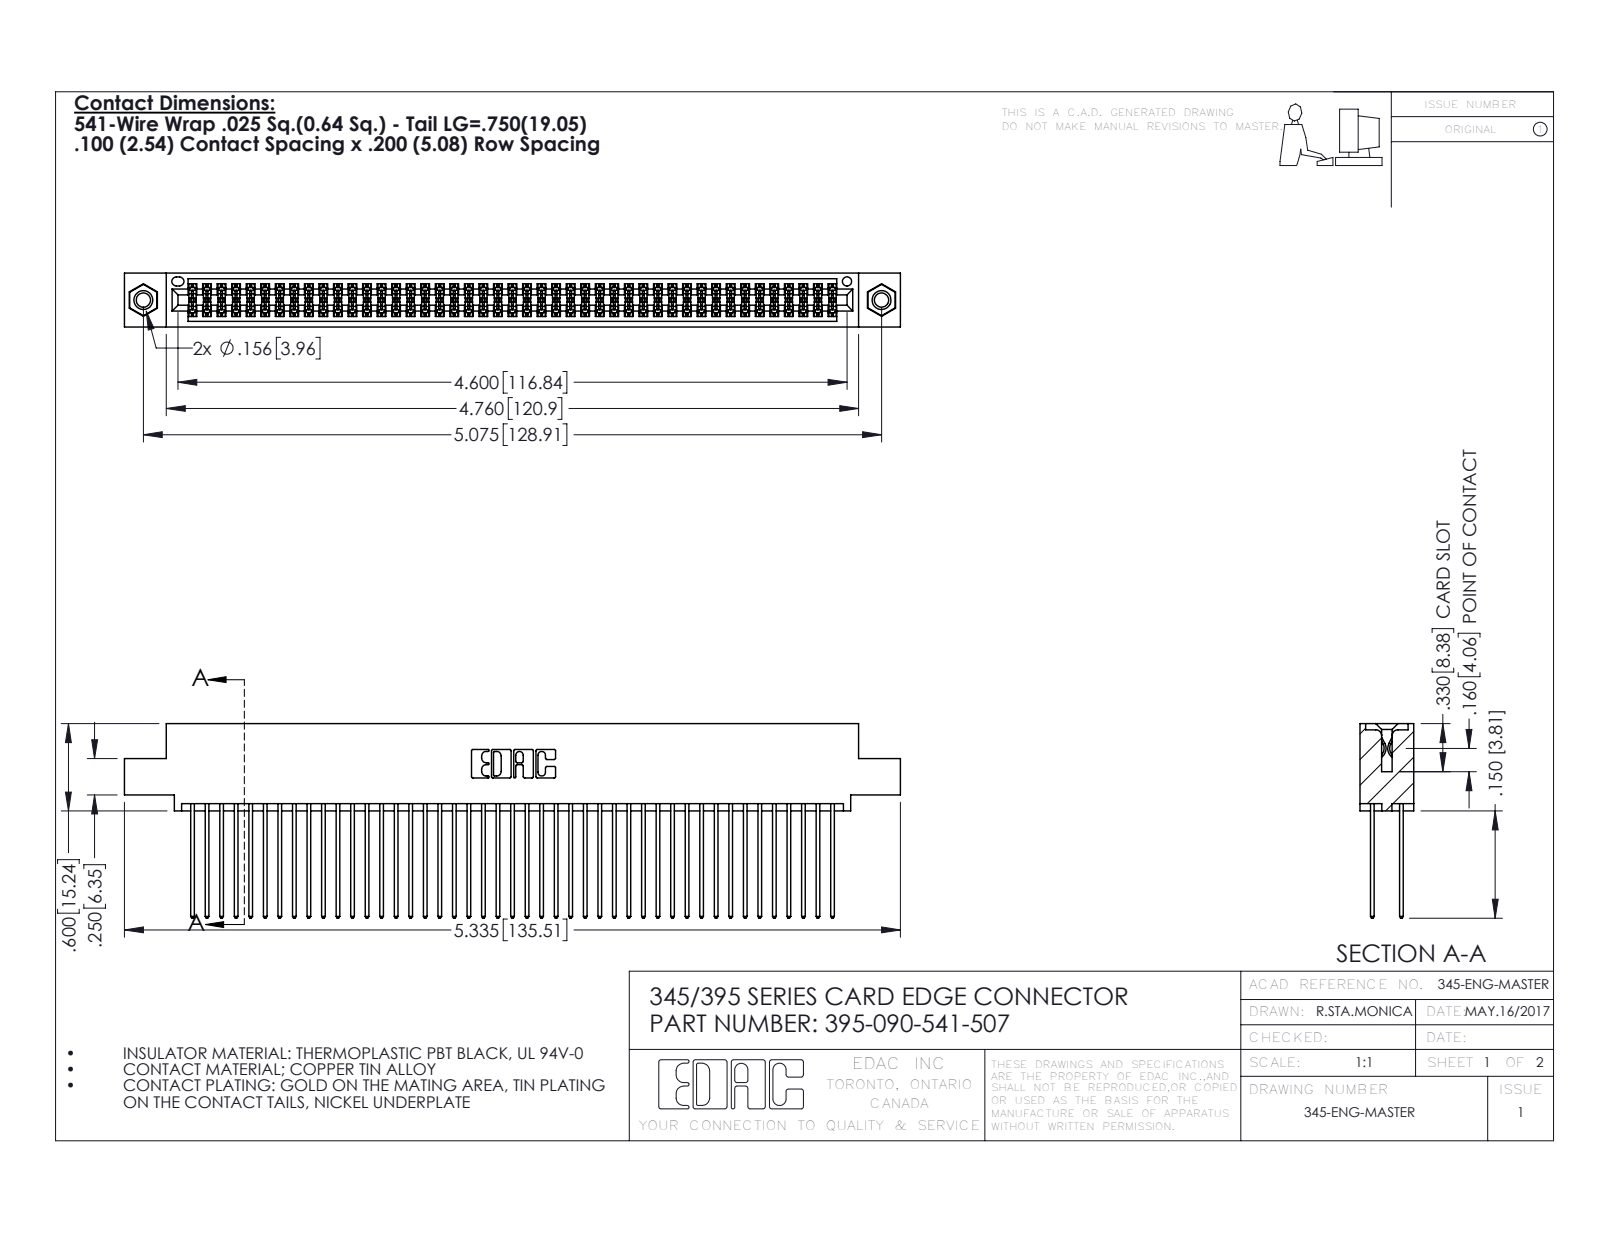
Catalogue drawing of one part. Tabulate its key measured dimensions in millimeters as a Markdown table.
| quantity | value |
| --- | --- |
| part name | 345-292-001_345-293-141; 395-090-541-507; 345-250-001_345-250-005-103; 345 Part_0.110 Offset - 0.156 Dia-TI |
| STEP written by | SolidWorks 2016 (CONFIG_CONTROL_DESIGN) |
| units | millimeters |
| bodies | 93 solids, 4690 faces (3086 planar, 1588 cylindrical, 16 other) |
| overall size | 135.5 × 34 × 9.4 |
| volume | 13 600 mm³ |
| surface area | 22 740 mm² |
| round holes (diameter × count) | 2.5 × 2, 3.2 × 2, 4 × 2, 1.6 × 1 |
| round bosses / shafts (diameter × count) | 3.9 × 2 |
| partial cylindrical surfaces (radius × count) | 0.2 × 135, 0.3 × 90, 0.3 × 22, 0.2 × 6, 0.8 × 6, 0.7 × 3, 0.4 × 2, 0.5 × 2 |
| main face-to-face distances | 1.8, 7.6, 5.1, 2.5, 6.9, 0.6, 5.7, 9.4, 4.4, 3.8 |
| hole center spacings | 6.9, 122.9, 128.9 |
